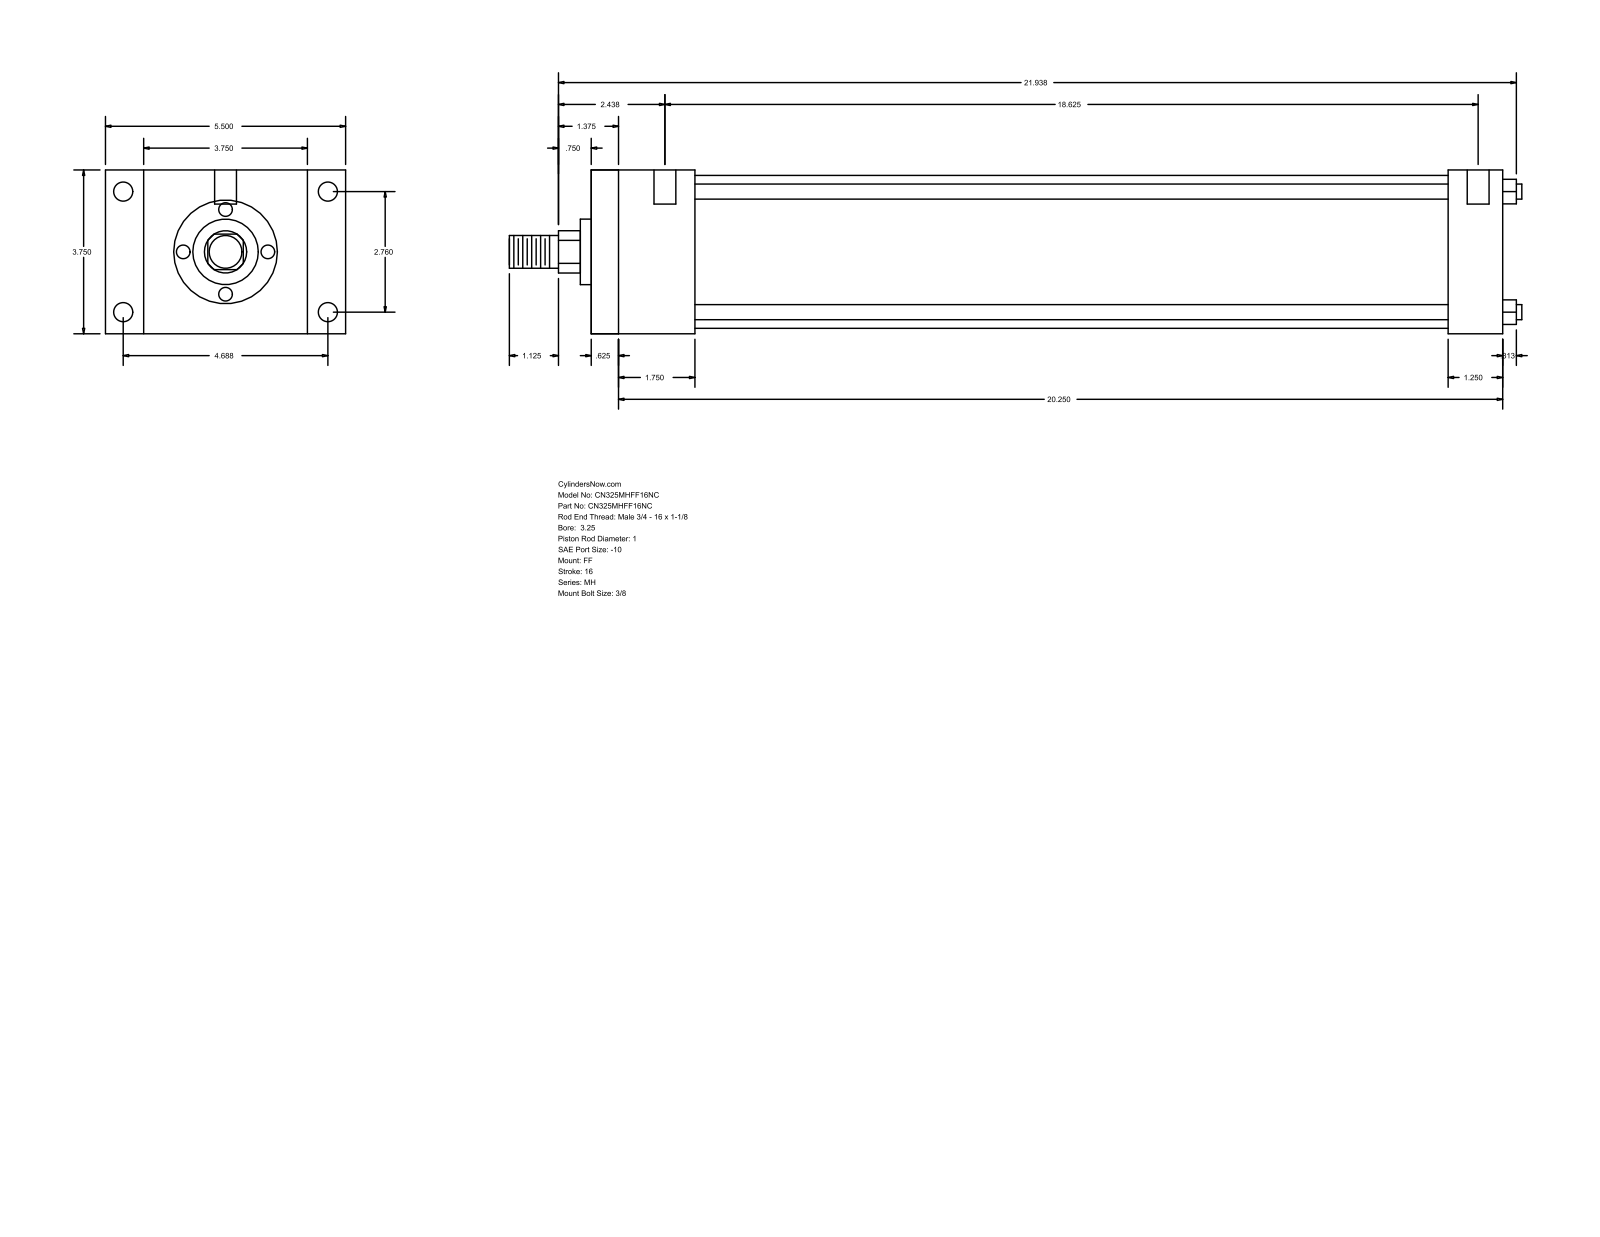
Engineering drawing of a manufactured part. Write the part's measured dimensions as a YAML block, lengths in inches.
part_name: "MH_FF__0325_1"
step_written_by: "GSSL Pune (CONFIG_CONTROL_DESIGN)"
units: inches
bodies: {solids: 0, faces: 92, planar: 64, cylindrical: 28, other: 0}
overall_size: [23.187, 5.5, 3.75]
round_holes:
  - {diameter: 0.219, count: 4}
  - {diameter: 0.438, count: 4}
  - {diameter: 0.5, count: 2}
round_bosses_or_shafts:
  - {diameter: 0.345, count: 4}
  - {diameter: 3.5, count: 1}
  - {diameter: 1.5, count: 1}
  - {diameter: 1, count: 1}
  - {diameter: 0.75, count: 1}
partial_cylinders:
  - {radius: 0.484, count: 1}
face_to_face_distances: [3.75, 20.875, 0.625, 20.25, 0.875, 4.625, 19.625, 19, 1.25, 2.375]
hole_center_spacings: [2.76, 4.687, 5.439, 18.875, 0.062, 0.187, 18.625, 18.687]
